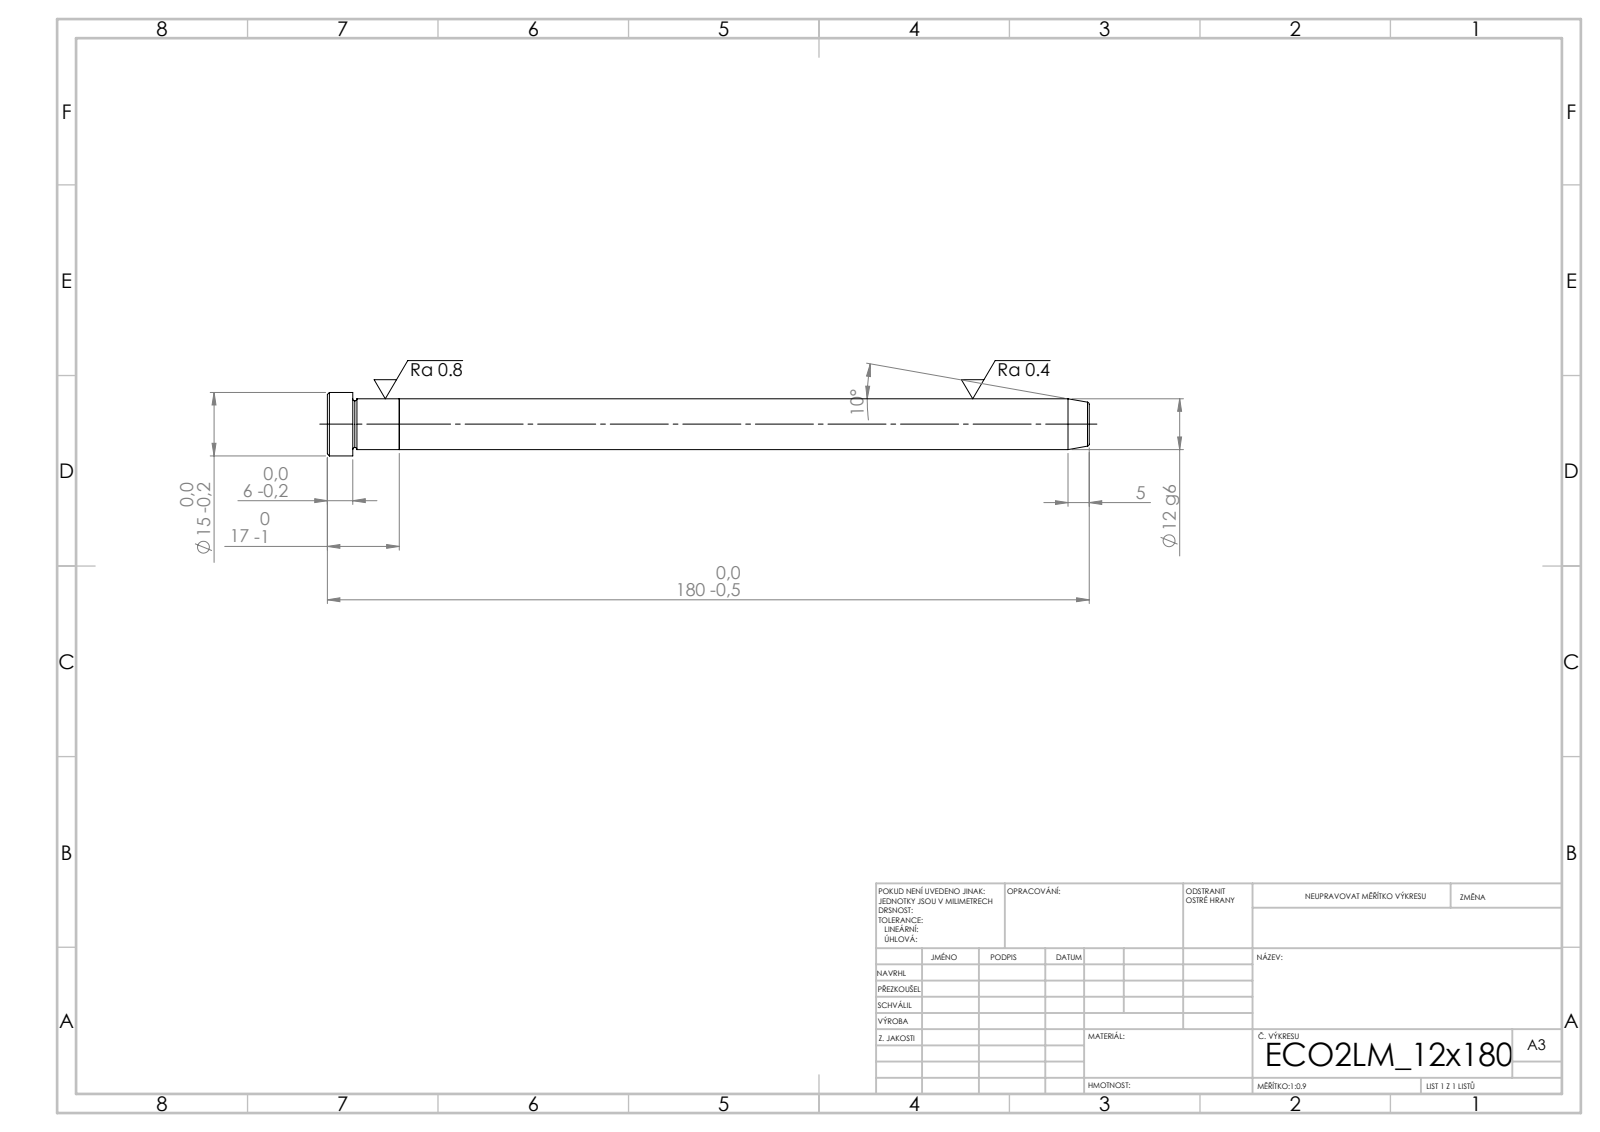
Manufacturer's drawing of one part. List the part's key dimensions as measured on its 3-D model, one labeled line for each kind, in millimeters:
STEP written by: SolidWorks 2019 (CONFIG_CONTROL_DESIGN)
Units: millimetres
Bodies: 2 solids, 21 faces (5 planar, 6 cylindrical, 10 other)
Overall size (bounding box): 180 × 15 × 15
Volume: 20 639 mm³ · Surface area: 7 380 mm²
Round bosses / shafts (diameter × count): ⌀15 ×1, ⌀12 ×1
Main face-to-face distances: 17, 163, 180, 174, 11, 6
